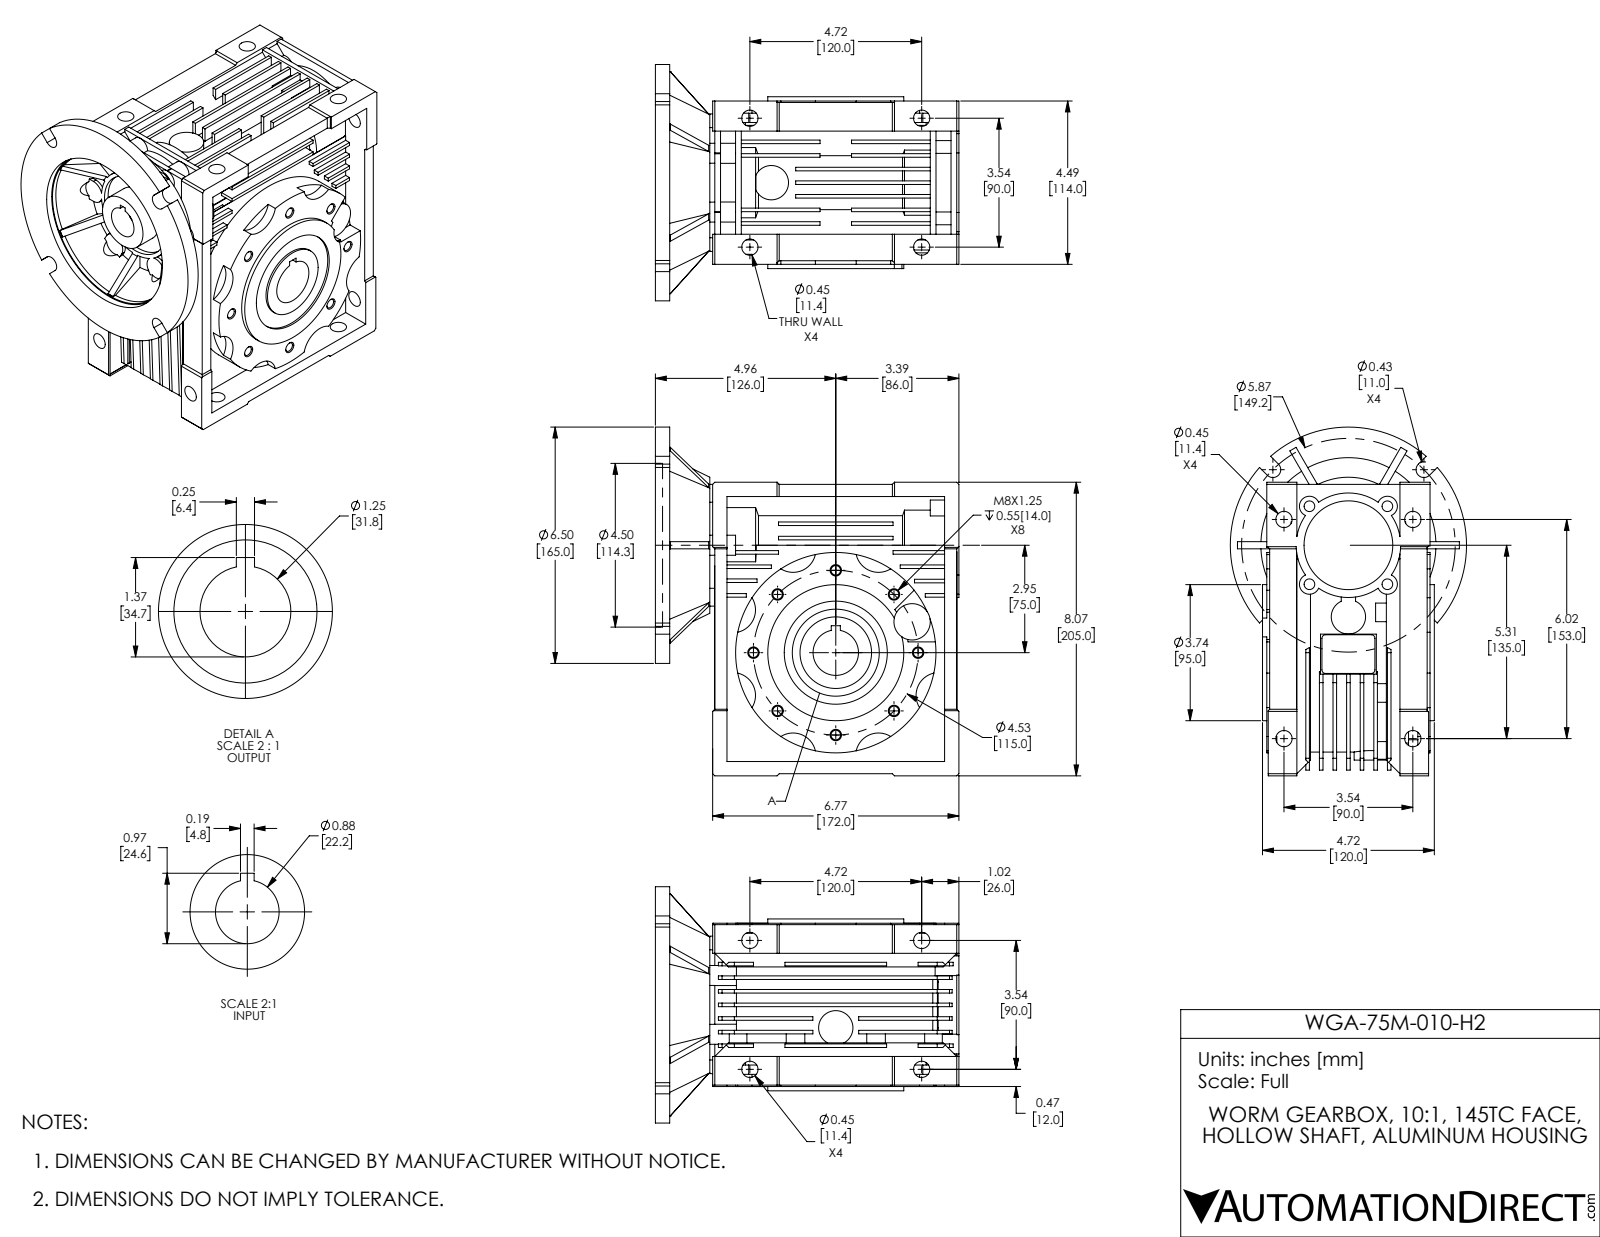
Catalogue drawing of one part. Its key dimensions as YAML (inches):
part_name: "WGA-75M-010-H2"
step_written_by: "SolidWorks 2021 (CONFIG_CONTROL_DESIGN)"
units: inches
bodies: {solids: 4, faces: 1179, planar: 675, cylindrical: 386, other: 118}
overall_size: [9.587, 8.346, 6.496]
volume: 180
surface_area: 782.1
round_holes:
  - {diameter: 0.262, count: 8}
  - {diameter: 0.448, count: 8}
  - {diameter: 0.293, count: 4}
  - {diameter: 0.875, count: 1}
  - {diameter: 0.906, count: 1}
  - {diameter: 1, count: 1}
  - {diameter: 1.25, count: 1}
  - {diameter: 1.535, count: 1}
  - {diameter: 1.654, count: 1}
  - {diameter: 1.969, count: 1}
  - {diameter: 2.441, count: 1}
  - {diameter: 2.677, count: 1}
round_bosses_or_shafts:
  - {diameter: 0.512, count: 14}
  - {diameter: 0.945, count: 3}
  - {diameter: 6.496, count: 1}
  - {diameter: 5.509, count: 1}
  - {diameter: 5.465, count: 1}
  - {diameter: 3.74, count: 1}
  - {diameter: 2.992, count: 1}
  - {diameter: 2.795, count: 1}
partial_cylinders:
  - {radius: 0.276, count: 10}
  - {radius: 0.63, count: 8}
  - {radius: 0.295, count: 6}
  - {radius: 0.335, count: 6}
  - {radius: 0.098, count: 4}
  - {radius: 0.217, count: 4}
  - {radius: 1.299, count: 1}
  - {radius: 1.417, count: 1}
face_to_face_distances: [0.374, 0.098, 0.472, 0.748, 0.276, 1.122, 1.496, 0.394, 0.65, 0.846]
hole_center_spacings: [2.264, 1.733, 3.202, 4.183, 1.515, 2.143, 3.543, 4.528]
